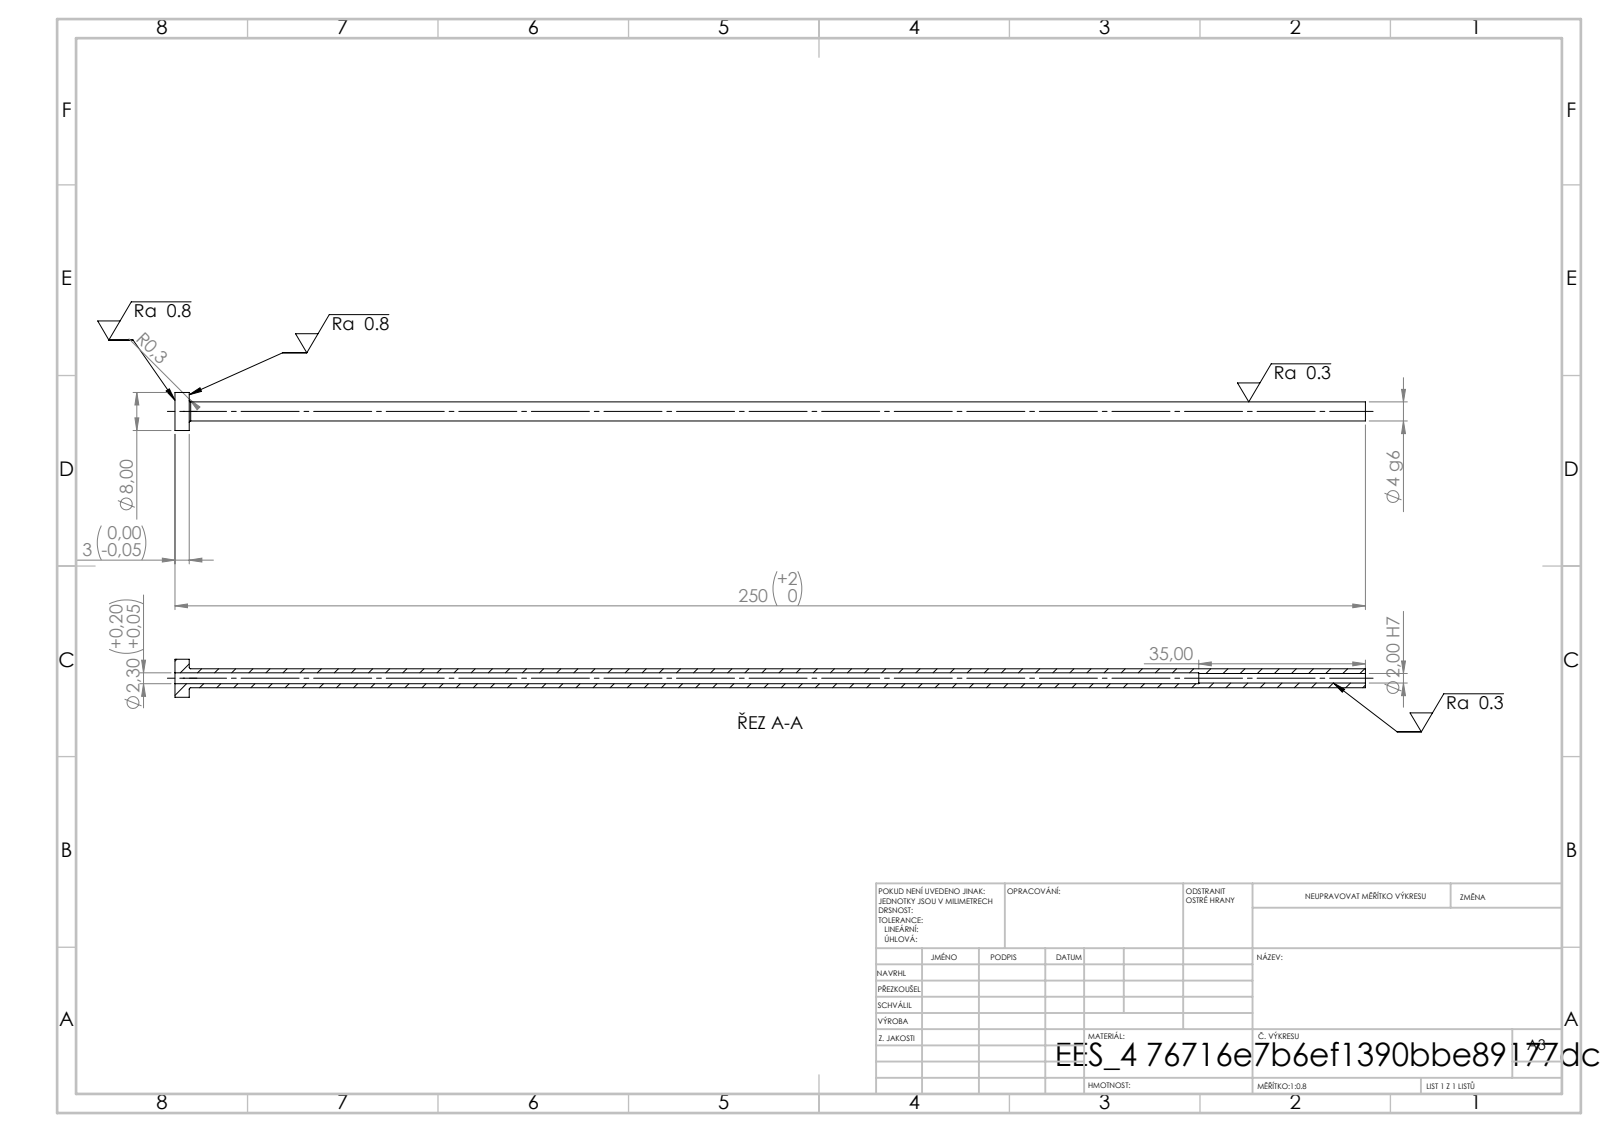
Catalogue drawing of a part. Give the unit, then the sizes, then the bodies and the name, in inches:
Units: inches
Overall size (bounding box): 9.843 × 0.315 × 0.315
Round holes (diameter × count): ⌀0.079 ×1, ⌀0.091 ×1
Round bosses / shafts (diameter × count): ⌀0.315 ×1, ⌀0.157 ×1
Main face-to-face distances: 0.118, 9.843, 9.724, 8.465, 8.346, 1.378
Volume: 0.137 in³ · Surface area: 7.82 in²
Bodies: 1 solid, 14 faces (4 planar, 8 cylindrical, 2 other)
STEP written by: SolidWorks 2019 (CONFIG_CONTROL_DESIGN)
